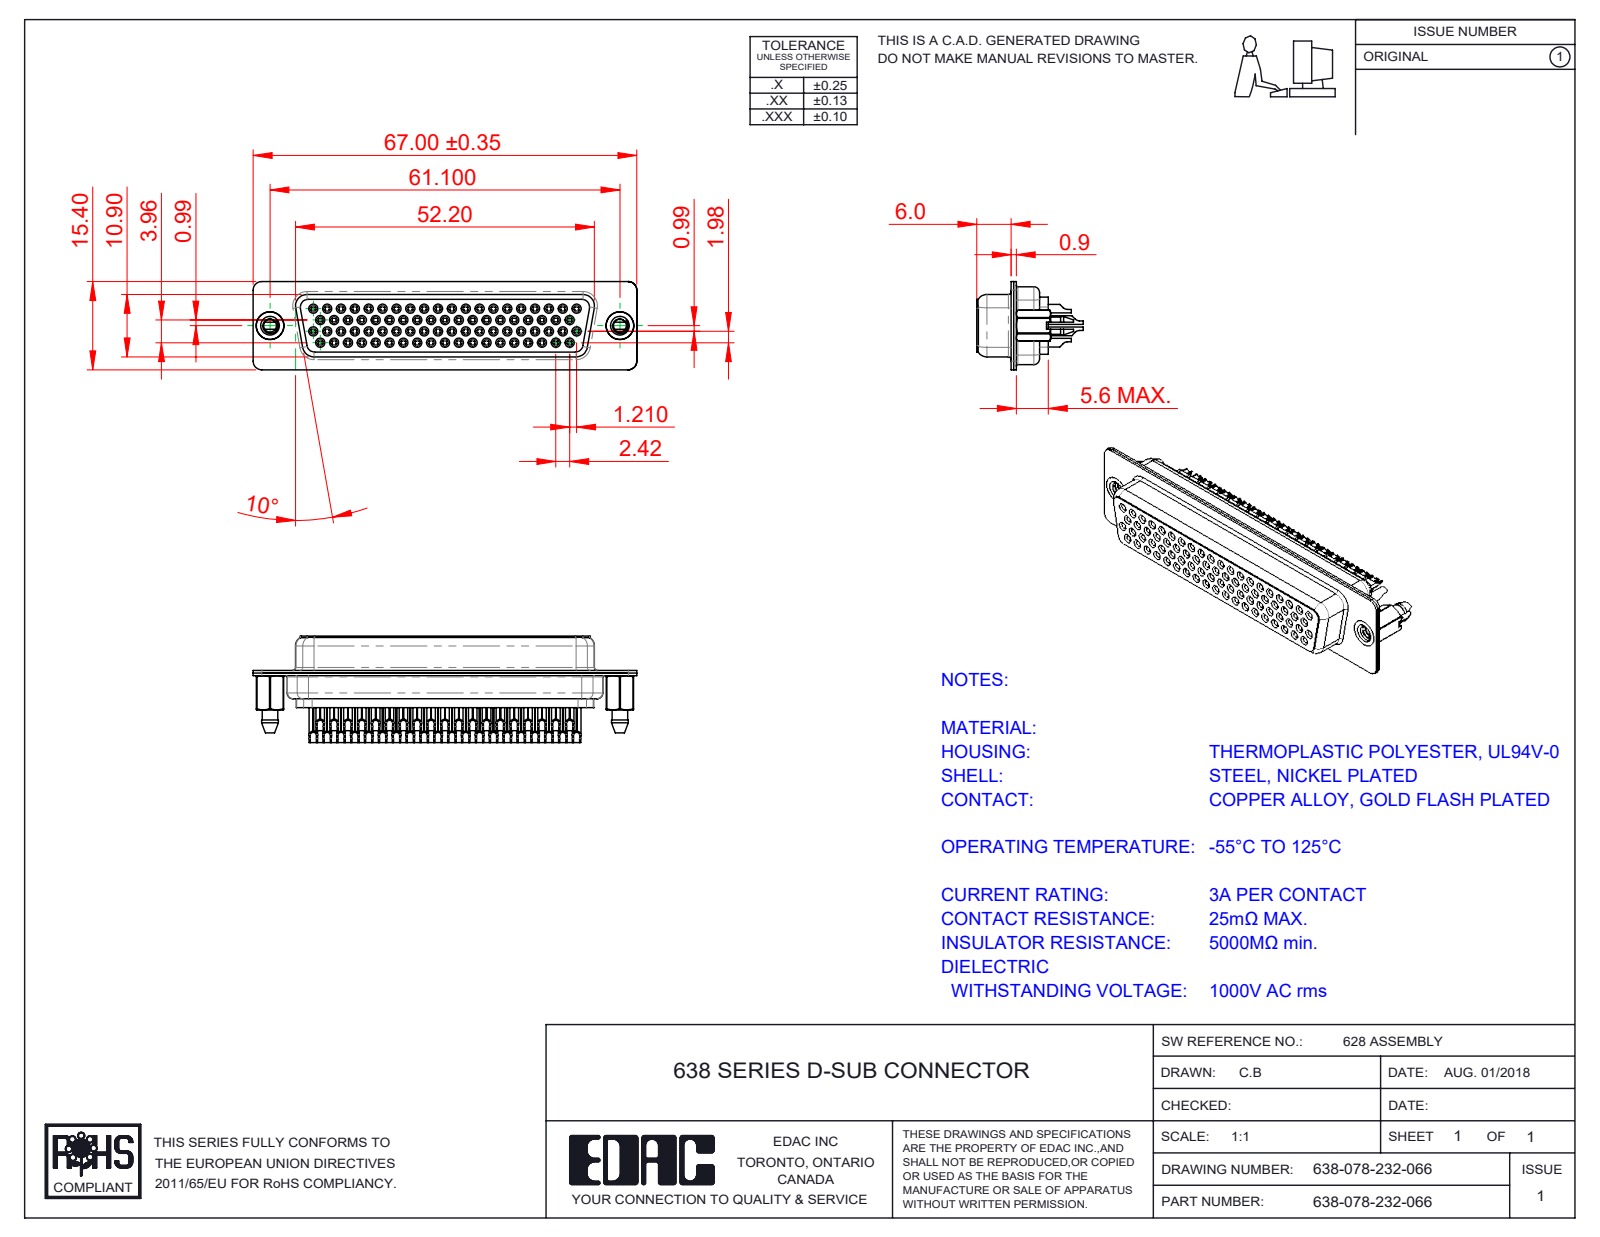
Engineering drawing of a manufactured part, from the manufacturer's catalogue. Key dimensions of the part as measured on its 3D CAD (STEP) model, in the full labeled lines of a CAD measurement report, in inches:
Part name (STEP PRODUCT): 638 Contact Row 2_32(78); 638 Contact Row 1_32(78); 638 Shell Front_78 Contacts; 638 Contact Row 78_32 (+5 more)
STEP written by: SolidWorks 2020 (CONFIG_CONTROL_DESIGN)
Units: inches
Bodies: 83 solids, 7295 faces (1737 planar, 2119 cylindrical, 3439 other)
Overall size (bounding box): 2.638 × 0.732 × 0.606
Volume: 0.375 in³ · Surface area: 34.73 in²
Round holes (diameter × count): ⌀0.031 ×78, ⌀0.039 ×78, ⌀0.043 ×78, ⌀0.063 ×78, ⌀0.067 ×78, ⌀0.071 ×78, ⌀0.089 ×2, ⌀0.157 ×2, ⌀0.159 ×2, ⌀0.191 ×2
Round bosses / shafts (diameter × count): ⌀0.079 ×78, ⌀0.059 ×78, ⌀0.047 ×78, ⌀0.195 ×2, ⌀0.189 ×2, ⌀0.157 ×1
Partial cylindrical surfaces — rounded edges, fillets, slot ends (radius × count): R0.011 ×39, R0.059 ×18, R0.079 ×12, R0.039 ×8, R0.061 ×8, R0.01 ×4, R0.02 ×4, R0.022 ×4
Main face-to-face distances: 0.018, 0.016, 0.035, 0.053, 0.378, 0.465, 0.071, 0.449, 0.087, 0.518
Hole centre spacings: 0.095, 0.191, 0.286, 0.381, 0.239, 0.476, 0.274, 0.334
